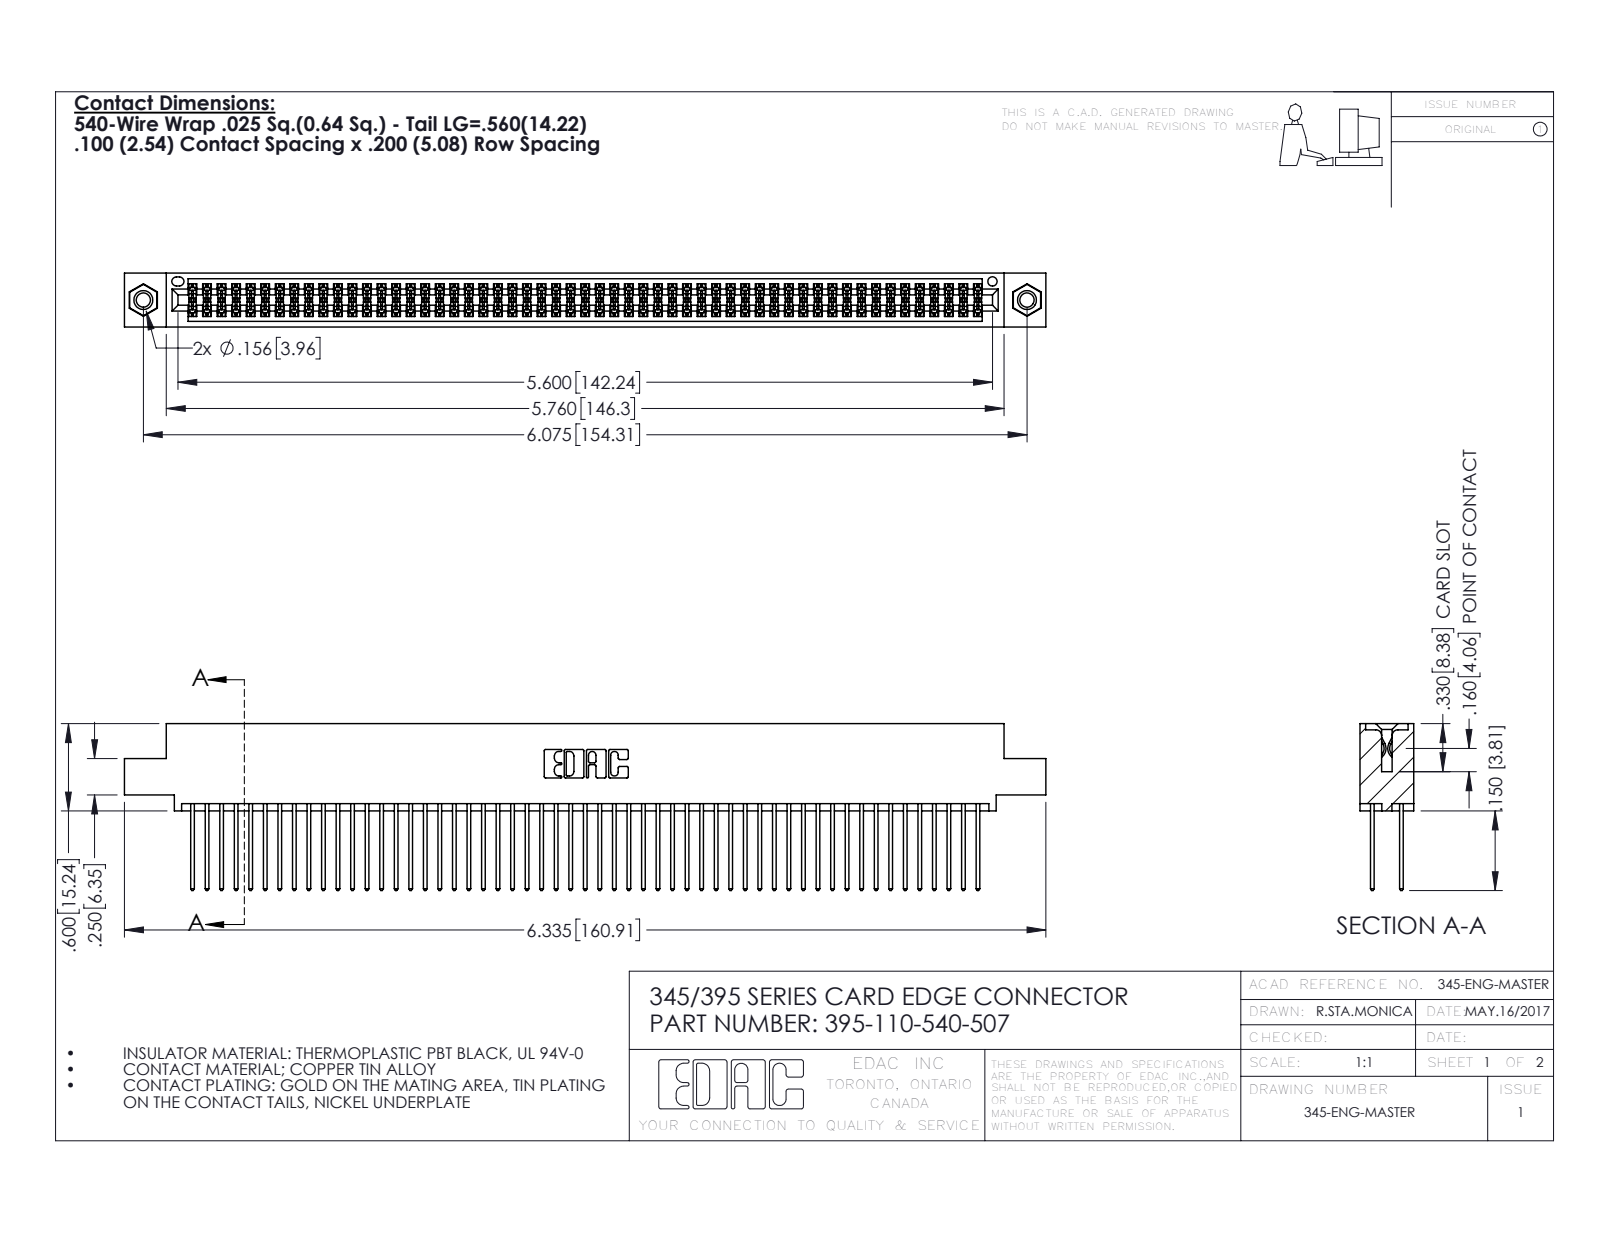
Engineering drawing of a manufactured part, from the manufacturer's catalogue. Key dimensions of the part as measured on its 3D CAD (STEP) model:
Part name (STEP PRODUCT): 345-292-001_345-293-140; 345 Part_0.110 Offset - 0.156 Dia-TI; 395-110-540-507; 345-250-001_345-250-005-103
STEP written by: SolidWorks 2016 (CONFIG_CONTROL_DESIGN)
Units: inches
Bodies: 113 solids, 5690 faces (3746 planar, 1928 cylindrical, 16 other)
Overall size (bounding box): 6.335 × 1.147 × 0.37
Volume: 0.981 in³ · Surface area: 40.42 in²
Round holes (diameter × count): ⌀0.098 ×2, ⌀0.125 ×2, ⌀0.156 ×2, ⌀0.064 ×1
Round bosses / shafts (diameter × count): ⌀0.155 ×2
Partial cylindrical surfaces — rounded edges, fillets, slot ends (radius × count): R0.006 ×165, R0.01 ×110, R0.01 ×22, R0.007 ×6, R0.031 ×6, R0.026 ×3, R0.014 ×2, R0.019 ×2
Main face-to-face distances: 0.072, 0.298, 0.2, 0.098, 0.272, 0.025, 0.37, 0.225, 0.175, 0.149
Hole centre spacings: 0.27, 5.839, 6.075
